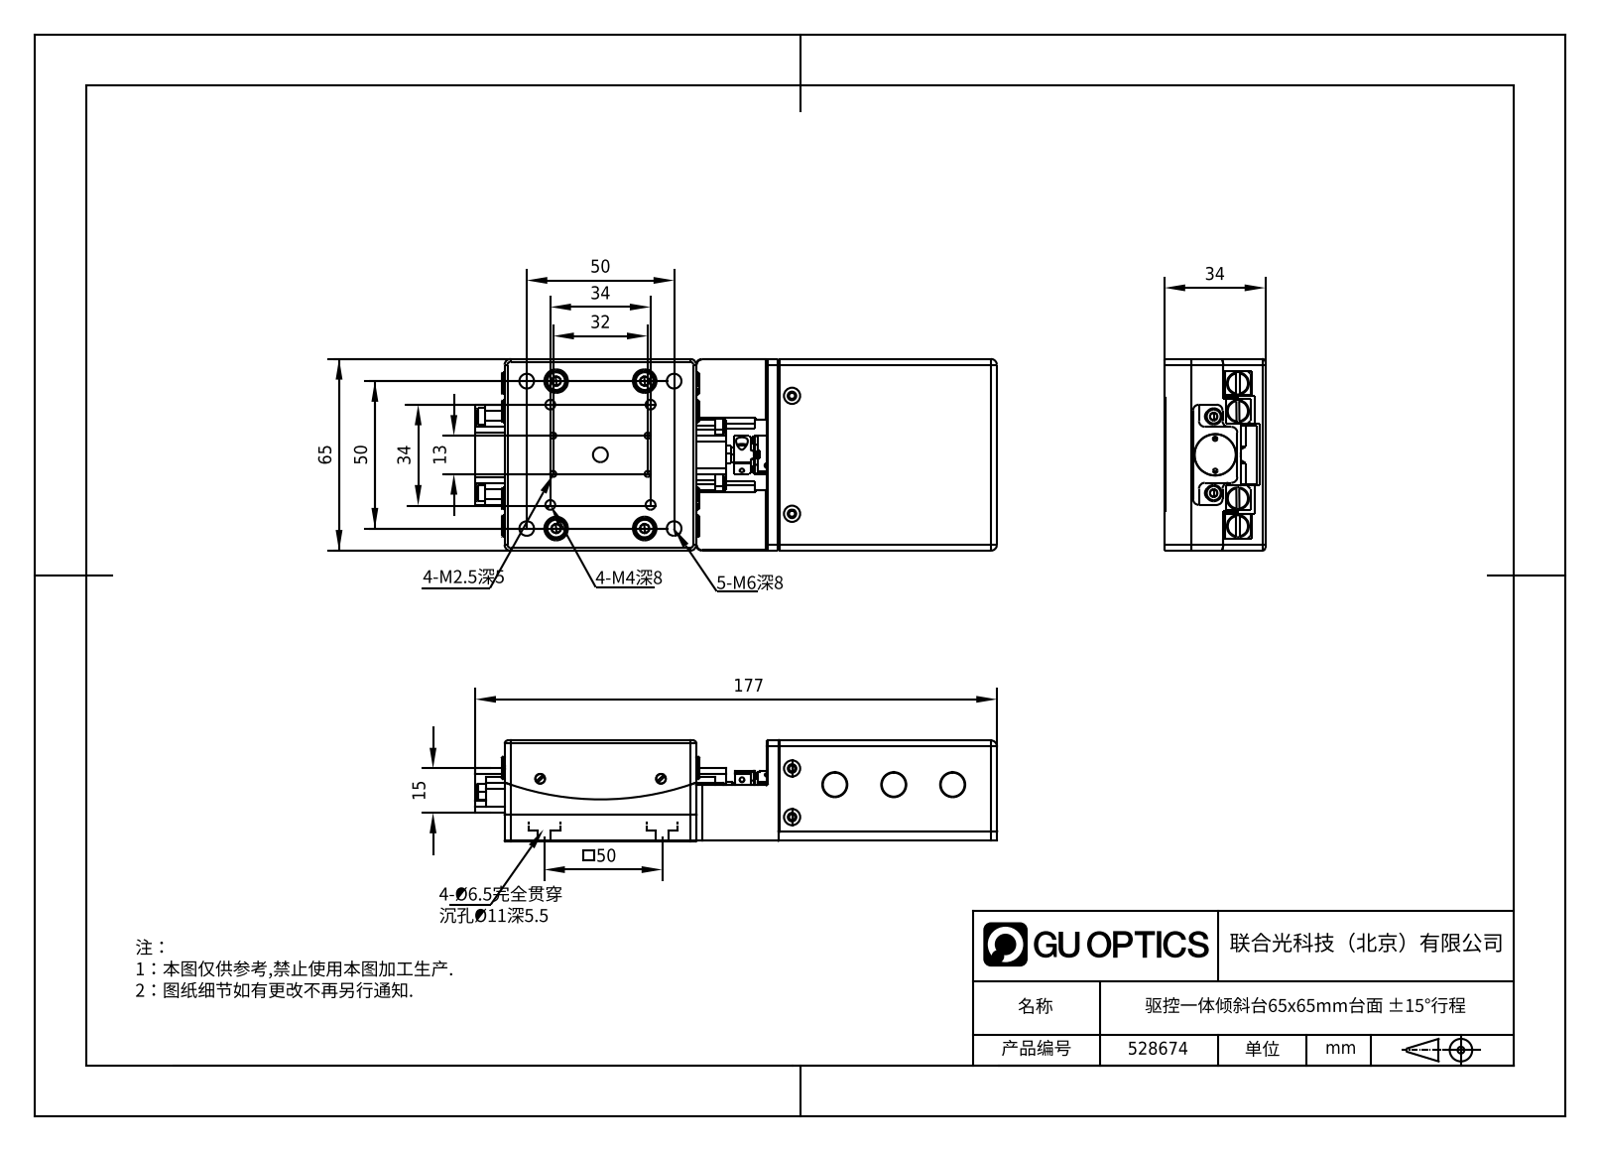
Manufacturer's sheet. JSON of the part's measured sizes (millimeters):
{"part_name": "528674", "step_written_by": "SolidWorks 2020 (CONFIG_CONTROL_DESIGN)", "units": "millimeters", "bodies": {"solids": 54, "faces": 1628, "planar": 672, "cylindrical": 627, "other": 329}, "overall_size": [177, 65, 34], "volume_mm3": 215021, "surface_area_mm2": 115375, "round_holes": [[3.3, 14], [2.05, 12], [5, 12], [2.5, 10], [2.9, 8], [4.5, 8], [3.2, 6], [11, 6], [2, 5], [3, 5], [5.5, 4], [6.5, 4]], "round_bosses_or_shafts": [[4, 10], [7, 8], [3, 8], [7.5, 4], [5.5, 4], [2.5, 4], [2.4, 4], [2.2, 4]], "partial_cylinders_radius": [[2, 47], [3, 6], [1, 4], [1.35, 4], [6.45, 1], [60, 1], [61, 1], [61.5, 1]], "face_to_face_distances": [3, 31, 2.5, 6, 34, 4, 65, 25, 9, 22.5], "hole_center_spacings": [13.21, 20.11, 20.52, 42.76, 7.57, 10, 39, 40]}
